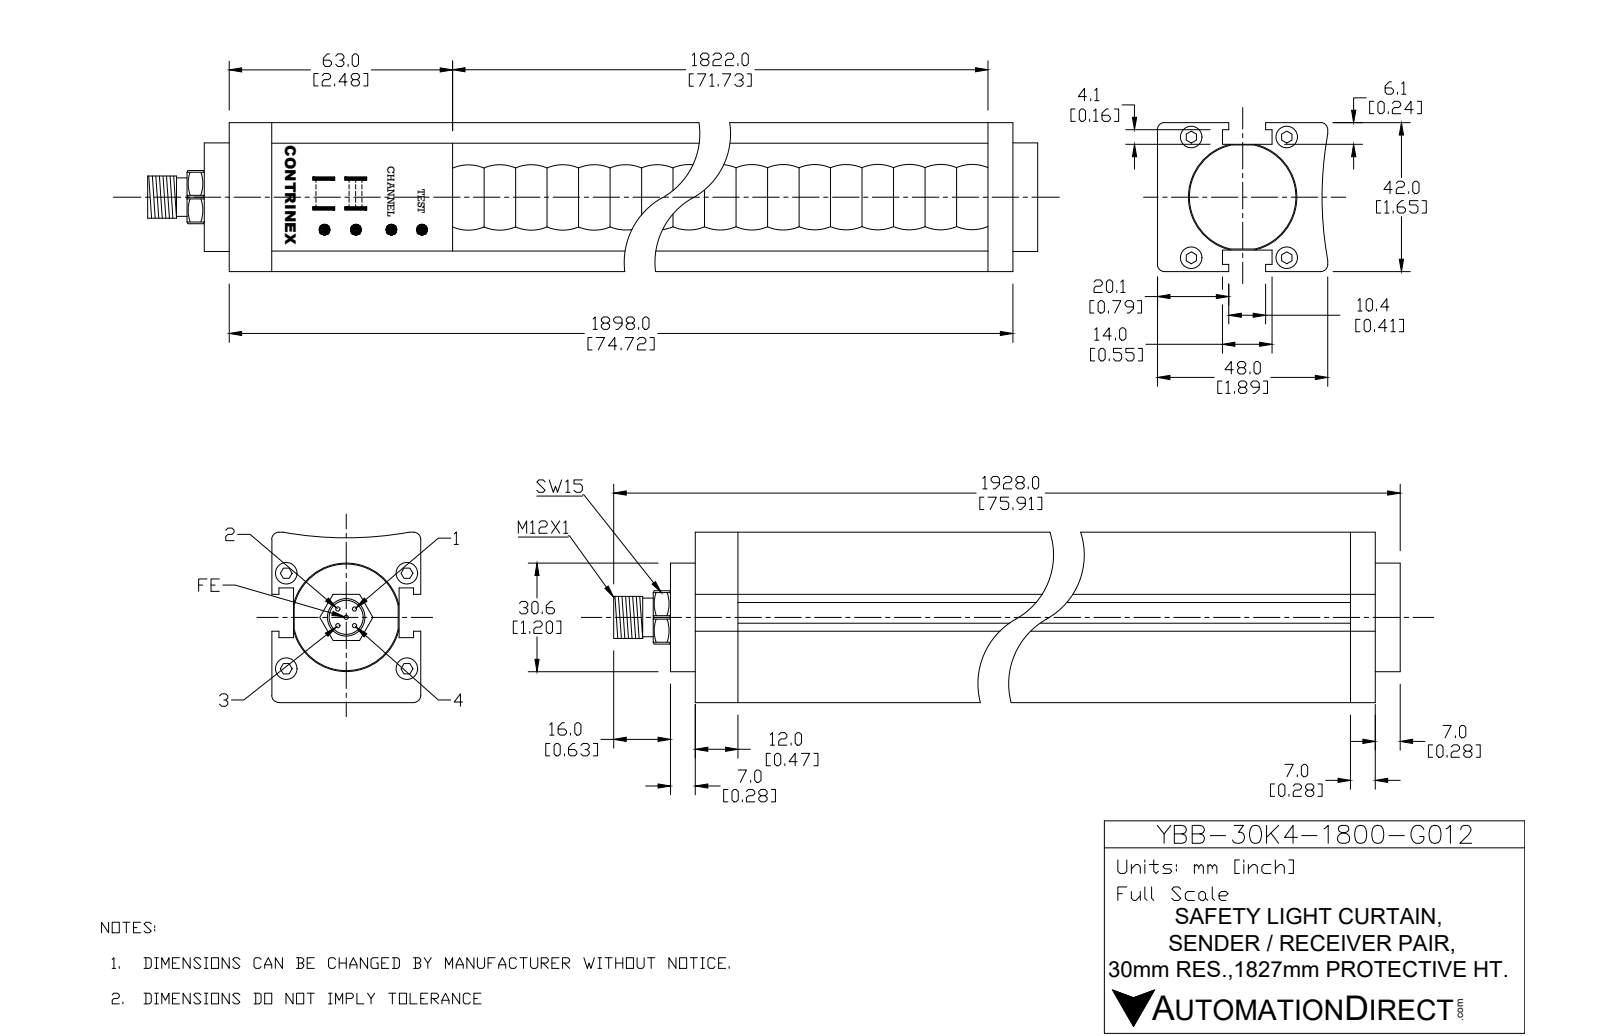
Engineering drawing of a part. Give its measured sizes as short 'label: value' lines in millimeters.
name: YBB-30K4-1800-G012
written by: SolidWorks 2019 (AUTOMOTIVE_DESIGN)
unit: mm
bodies: 1 solid, 533 faces (121 planar, 152 cylindrical, 260 other)
size: 1928 × 48 × 42
volume: 3 189 000 mm³; area: 550 600 mm²
holes: 4× ⌀3, 4× ⌀6, 1× ⌀8.5
bosses: 5× ⌀1, 4× ⌀5.5, 4× ⌀3, 1× ⌀30.6, 1× ⌀12, 1× ⌀10.5
rounds: 36× R0.9, 12× R1, 10× R0.4, 2× R5.5, 1× R0.5, 1× R0.5, 1× R8.2, 1× R17.5
face distances: 5.9, 36.1, 42, 30.3, 46.4, 55.2, 50.9, 5.1, 36.9, 0.8
hole spacings: 21, 22.4, 26.9, 34, 43.4
